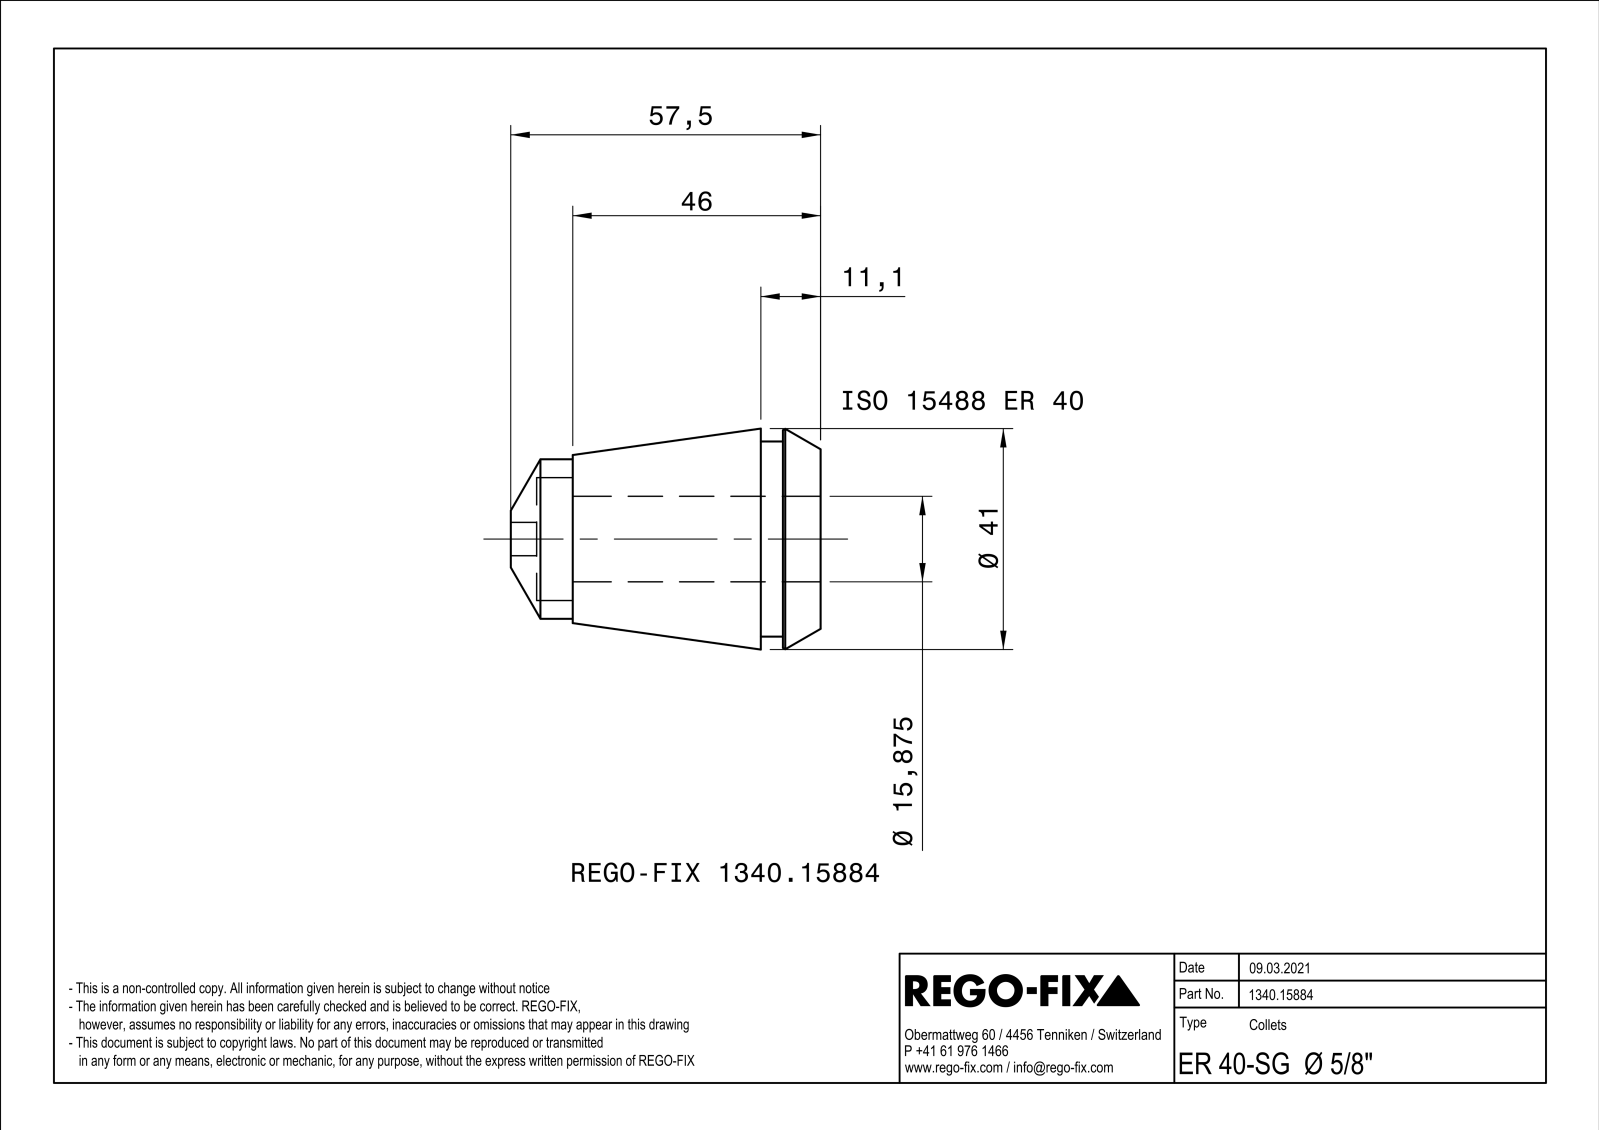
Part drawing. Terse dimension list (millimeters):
name: NOCUT
written by: SIEMENS PLM Software Solid Edge ST10 (AUTOMOTIVE_DESIGN)
unit: mm
bodies: 1 solid, 283 faces (151 planar, 36 cylindrical, 96 other)
size: 61.8 × 40.85 × 40.85
volume: 36 027 mm³; area: 22 446 mm²
holes: 1× ⌀3, 1× ⌀15.88, 1× ⌀22.8, 1× ⌀25, 1× ⌀26, 1× ⌀28.2
bosses: 1× ⌀36.2, 1× ⌀29.6, 1× ⌀25.8, 1× ⌀25.5, 1× ⌀24.8, 1× ⌀7, 1× ⌀4.4
rounds: 1× R3.09
face distances: 1, 52.7, 44, 8.7, 7, 37, 45.7, 4.1, 11.1, 32.9
